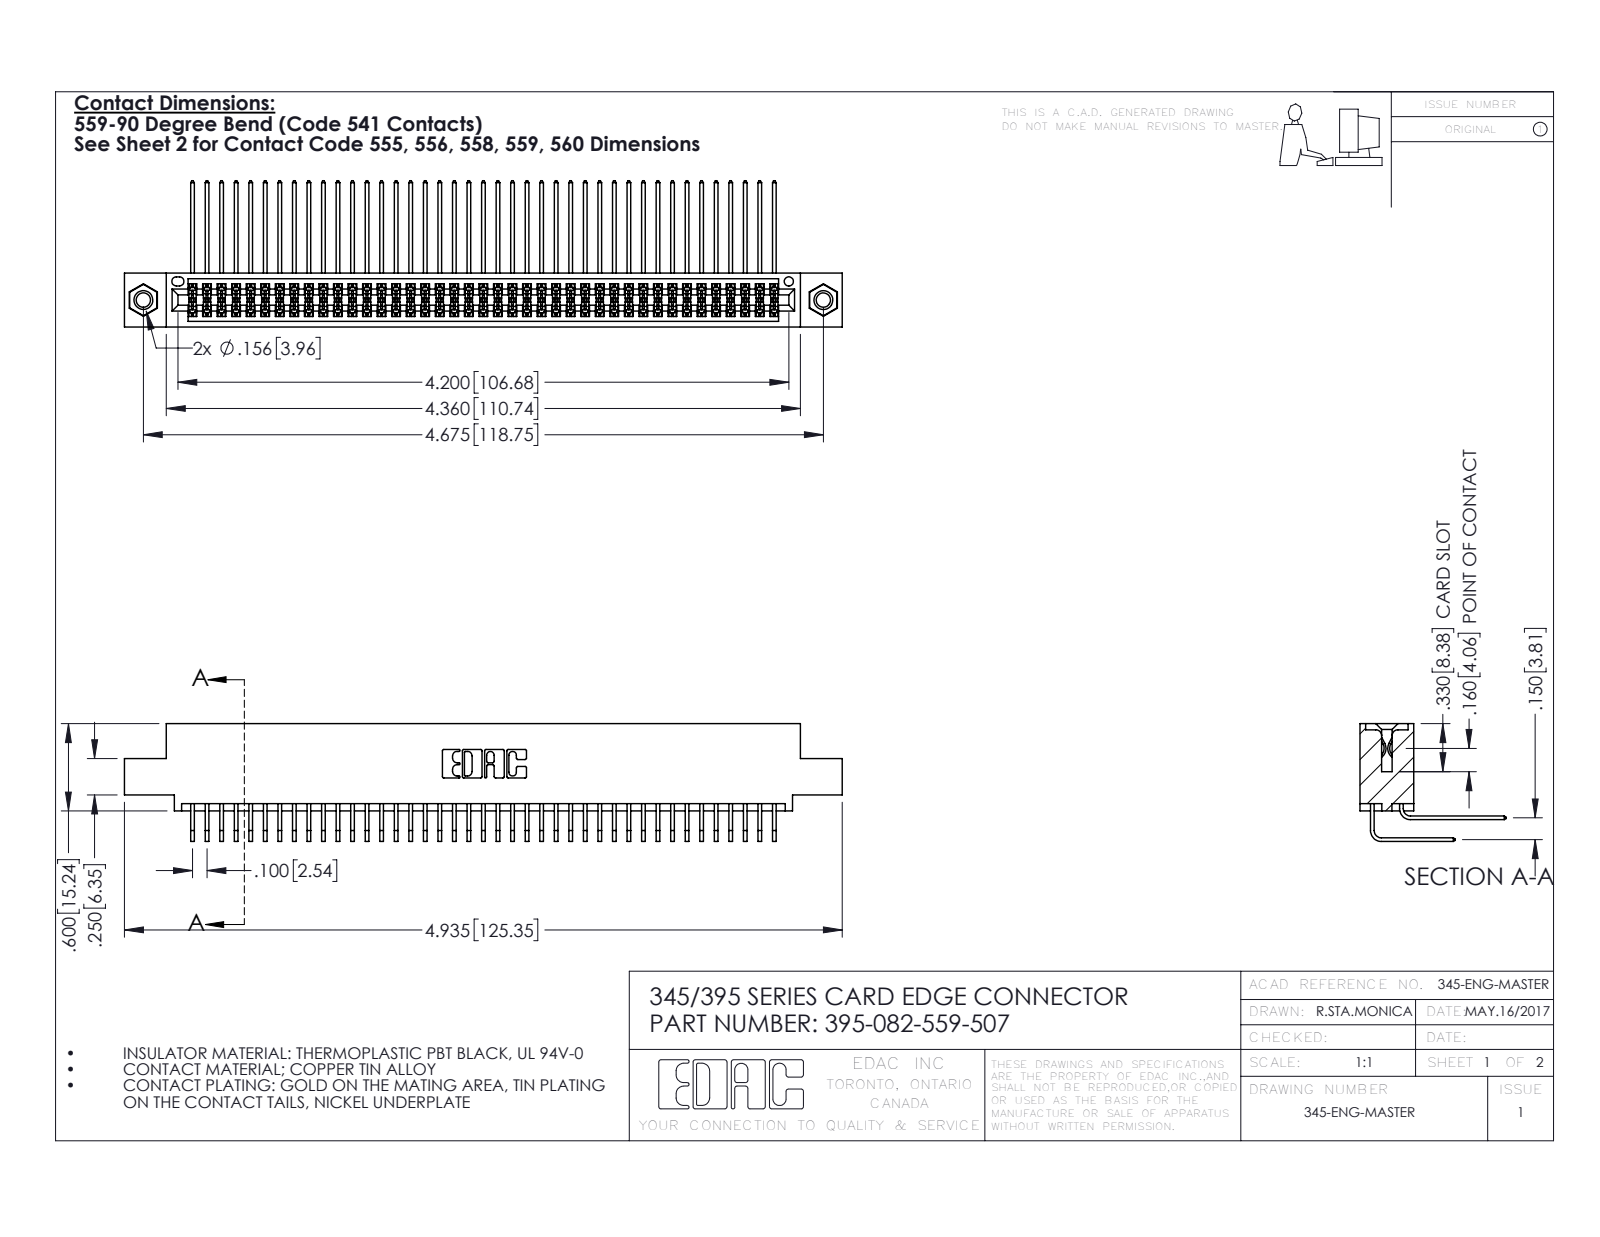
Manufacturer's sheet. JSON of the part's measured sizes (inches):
{"part_name": "345 Part_0.110 Offset - 0.156 Dia-TI; 345-292-001_558 559 Tail - 1; 345-250-001_345-250-005-103; 345-292-001_559 Tail - 2 (+1 more)", "step_written_by": "SolidWorks 2016 (CONFIG_CONTROL_DESIGN)", "units": "inches", "bodies": {"solids": 85, "faces": 4454, "planar": 2986, "cylindrical": 1452, "other": 16}, "overall_size": [4.935, 1.005, 0.809], "volume_in3": 0.766, "surface_area_in2": 32.37, "round_holes": [[0.098, 2], [0.125, 2], [0.156, 2], [0.064, 1]], "round_bosses_or_shafts": [[0.155, 2]], "partial_cylinders_radius": [[0.006, 123], [0.01, 22], [0.007, 6], [0.031, 6], [0.026, 3], [0.014, 2], [0.019, 2], [0.022, 2]], "face_to_face_distances": [0.072, 0.298, 0.2, 0.37, 0.098, 0.272, 0.025, 0.225, 0.175, 0.15], "hole_center_spacings": [0.27, 4.439, 4.675]}
